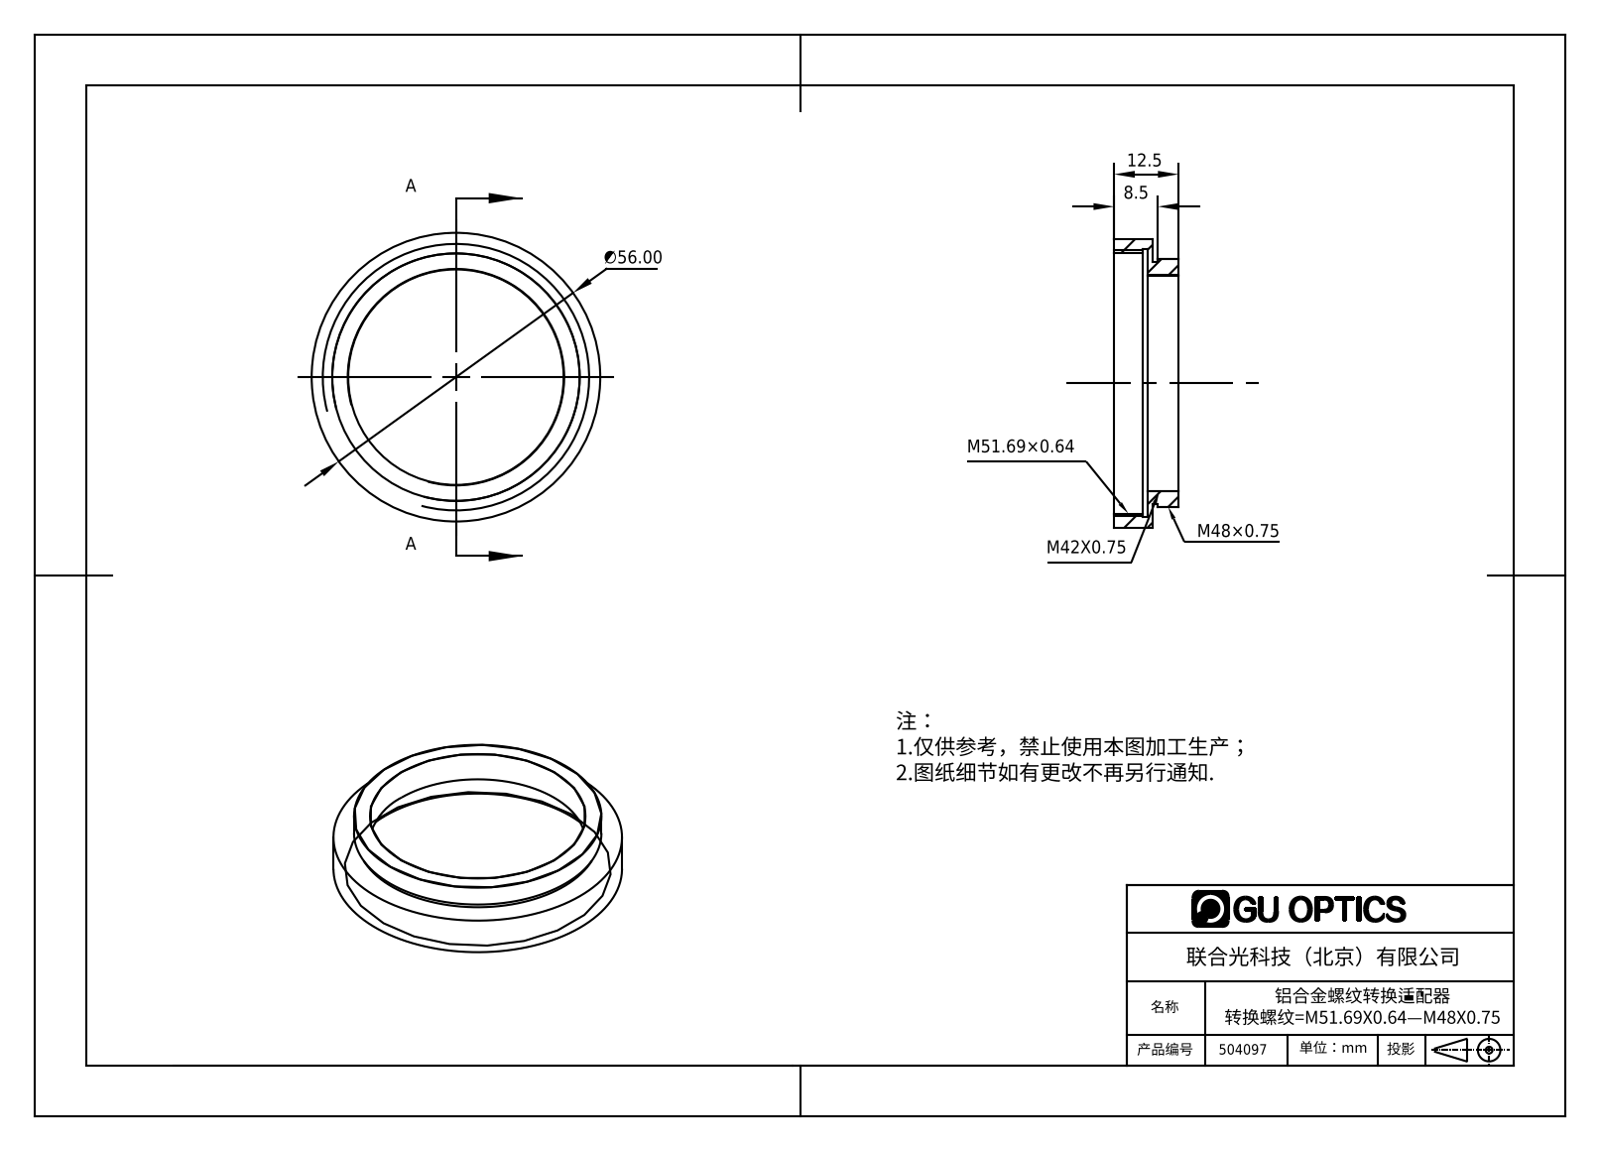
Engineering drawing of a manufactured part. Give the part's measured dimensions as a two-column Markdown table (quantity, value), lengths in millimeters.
| quantity | value |
| --- | --- |
| part name | 504097 |
| STEP written by | SolidWorks 2016 (AUTOMOTIVE_DESIGN) |
| units | millimeters |
| bodies | 1 solid, 18 faces (6 planar, 12 cylindrical, 0 other) |
| overall size | 56 × 56 × 12.5 |
| volume | 6 043 mm³ |
| surface area | 6 439 mm² |
| round holes (diameter × count) | 41.8 × 1, 50.6 × 1, 51.9 × 1 |
| round bosses / shafts (diameter × count) | 56 × 1, 48.02 × 1, 47 × 1 |
| main face-to-face distances | 1, 6.5, 7.5, 12.5, 6, 5, 2, 5.5, 7, 8.5 |
